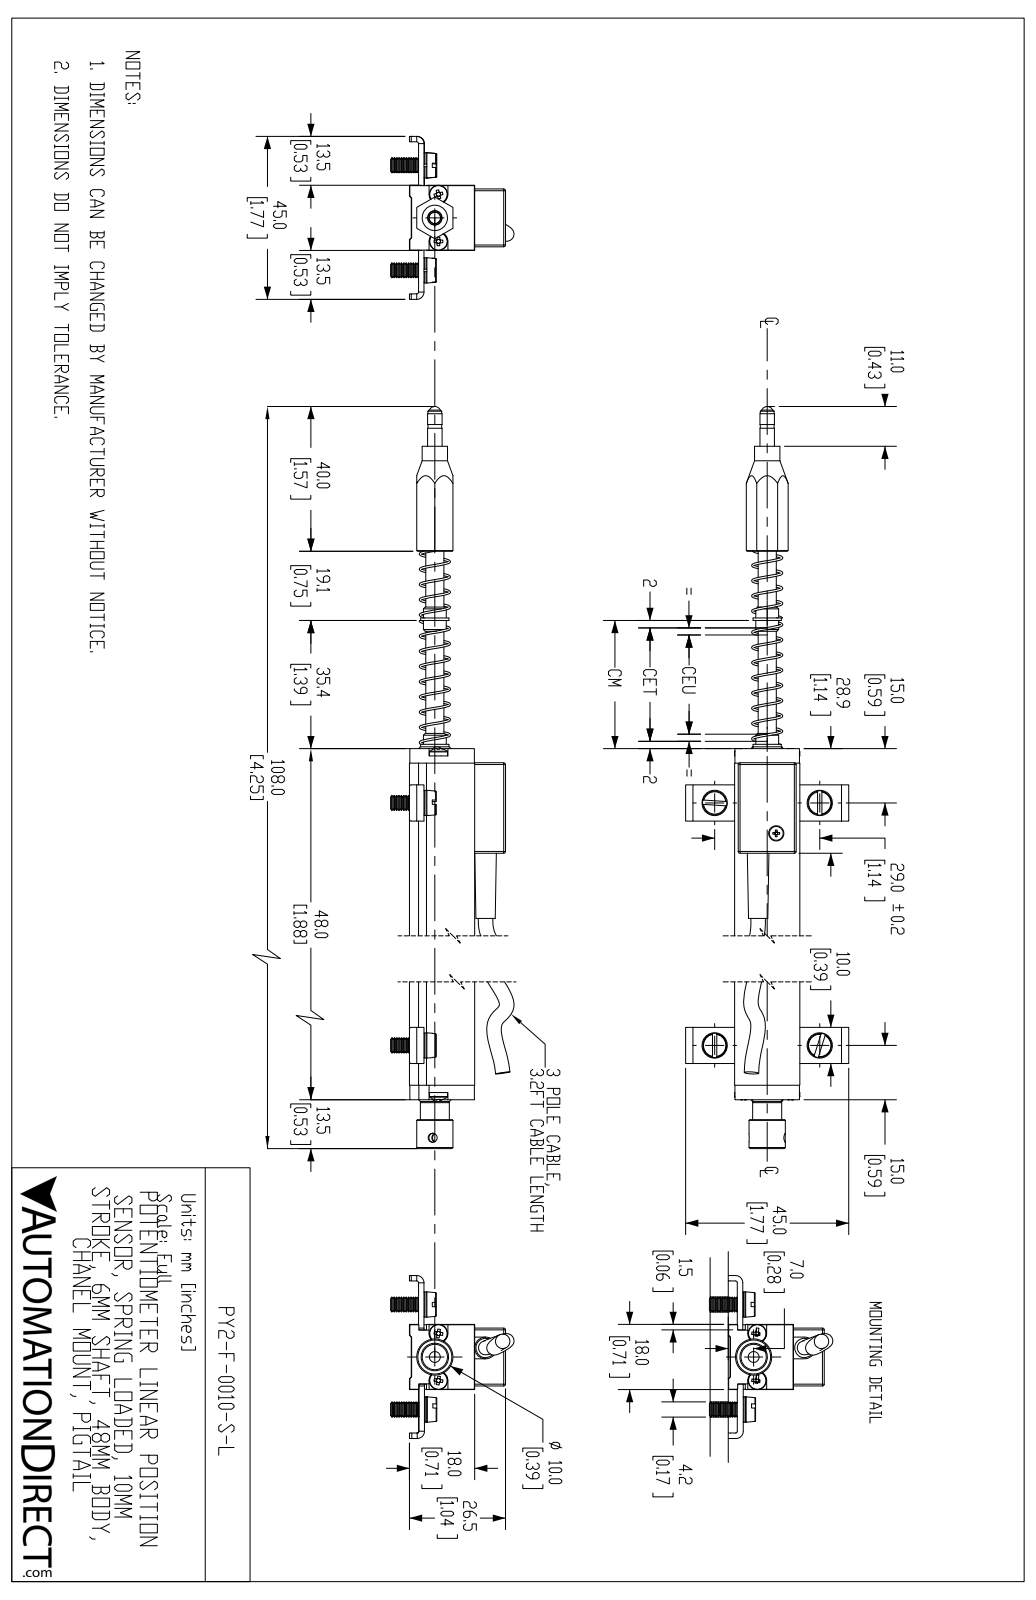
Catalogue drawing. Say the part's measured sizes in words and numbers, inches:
The part is named "PY2-F-0010-S-L". Its 3-D file was written by "SolidWorks 2019 (AUTOMOTIVE_DESIGN)". It is 31 solids with 969 faces: 323 planar, 247 cylindrical and 399 other. Overall it measures 5.015 by 1.772 by 1.34 inches. Its volume is 1.415 cubic inches and its surface area 26.8 square inches. Round holes: 4 of diameter 0.142, 4 of diameter 0.169, 2 of diameter 0.091, 2 of diameter 0.098, 2 of diameter 0.106, 2 of diameter 0.236, 1 of diameter 0.063, 1 of diameter 0.079, 1 of diameter 0.081, 1 of diameter 0.083, 1 of diameter 0.102, 1 of diameter 0.13. Round bosses or shafts: 6 of diameter 0.157, 4 of diameter 0.274, 3 of diameter 0.197, 3 of diameter 0.098, 2 of diameter 0.15, 1 of diameter 0.394, 1 of diameter 0.315, 1 of diameter 0.307. Partial cylindrical surfaces (rounded edges, fillets, slot ends): 25 of radius 0.02, 4 of radius 0.079, 2 of radius 0.102, 1 of radius 0.177. The main face-to-face distances are 0.709, 0.059, 0.079, 0.157, 0.039, 0.61, 0.02, 1.732, 1.575, 0.65. The hole center spacings are 0.259, 0.574, 0.709, 0.96, 1.142, 1.344, 0.406, 0.512.
